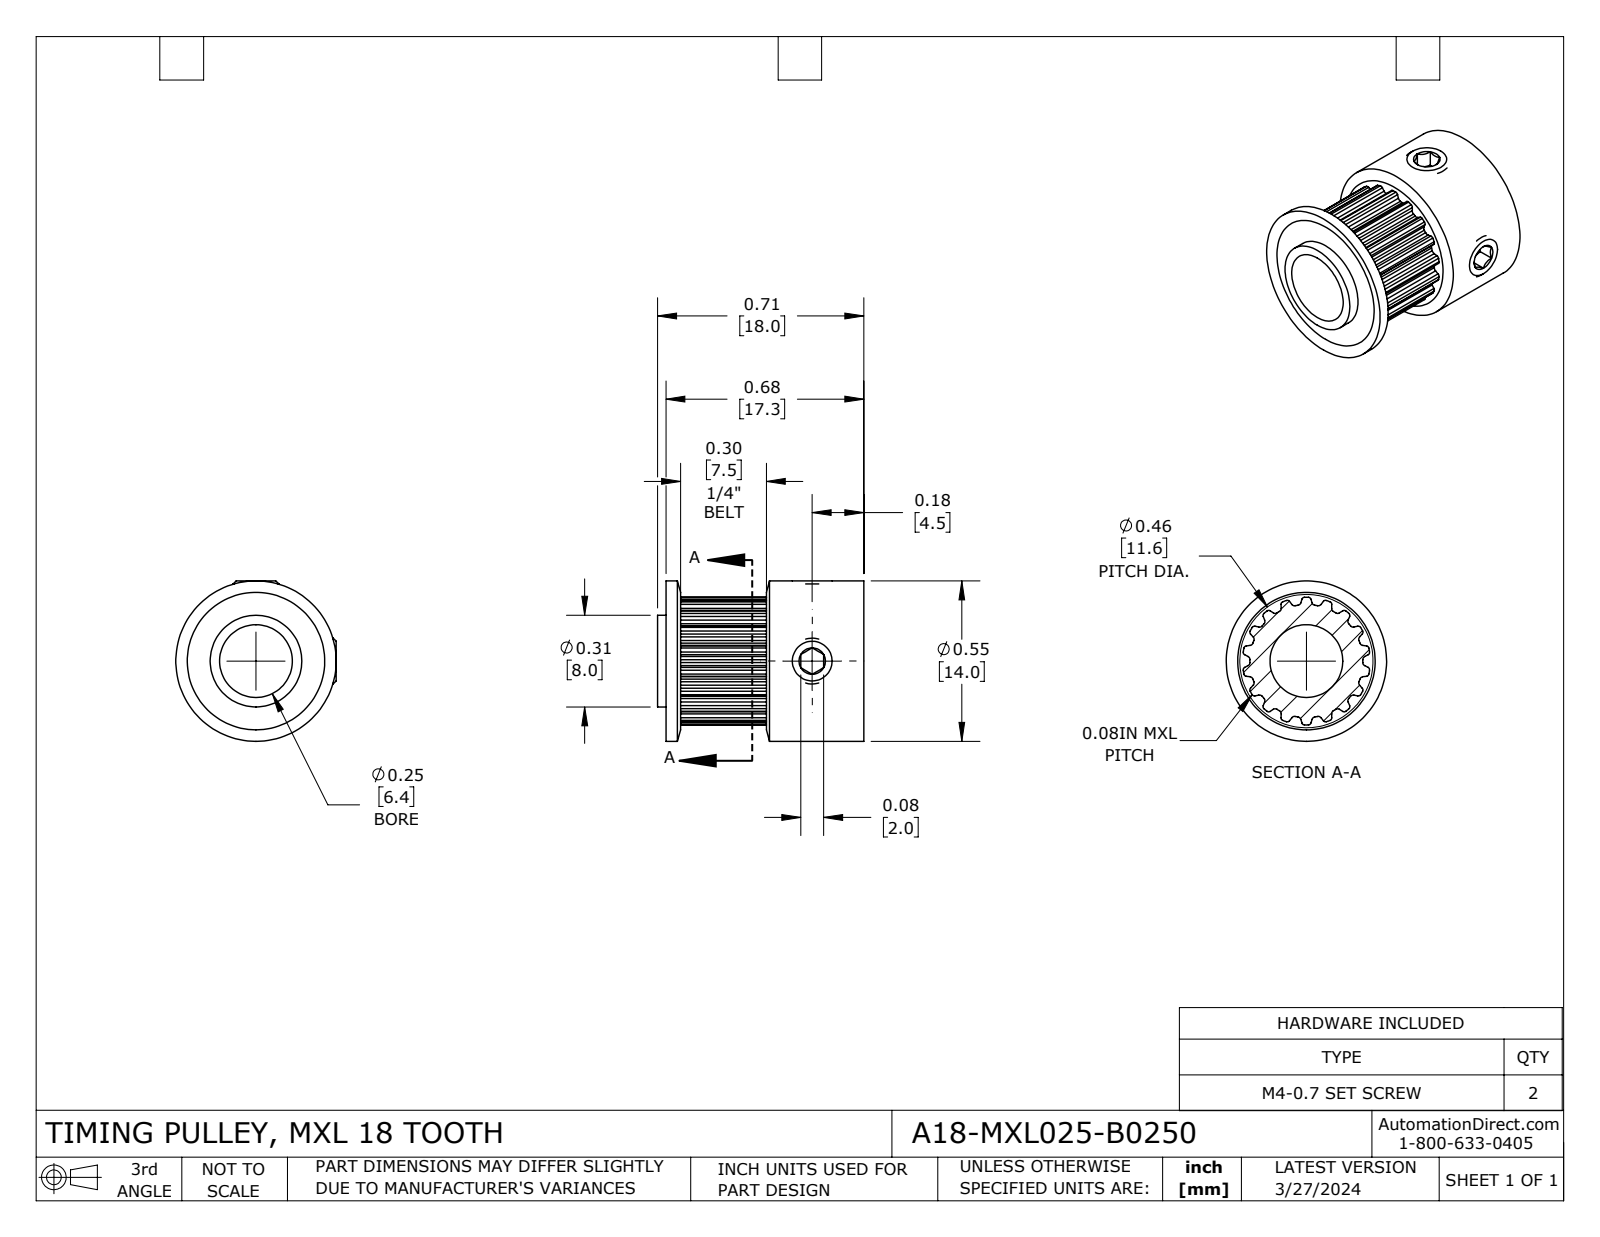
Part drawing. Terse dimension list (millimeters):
name: A18-MXL025-B0250
written by: SolidWorks 2021 (CONFIG_CONTROL_DESIGN)
unit: mm
bodies: 3 solids, 226 faces (57 planar, 137 cylindrical, 32 other)
size: 18 × 14 × 14
volume: 1 577 mm³; area: 1 690 mm²
holes: 2× ⌀3.3, 1× ⌀6.35
bosses: 2× ⌀4, 1× ⌀14, 1× ⌀8
rounds: 36× R0.23, 36× R0.3, 1× R4.93, 1× R5.57
face distances: 17, 8.5, 4.08, 1, 2, 16, 7.5, 9.5, 18, 3
